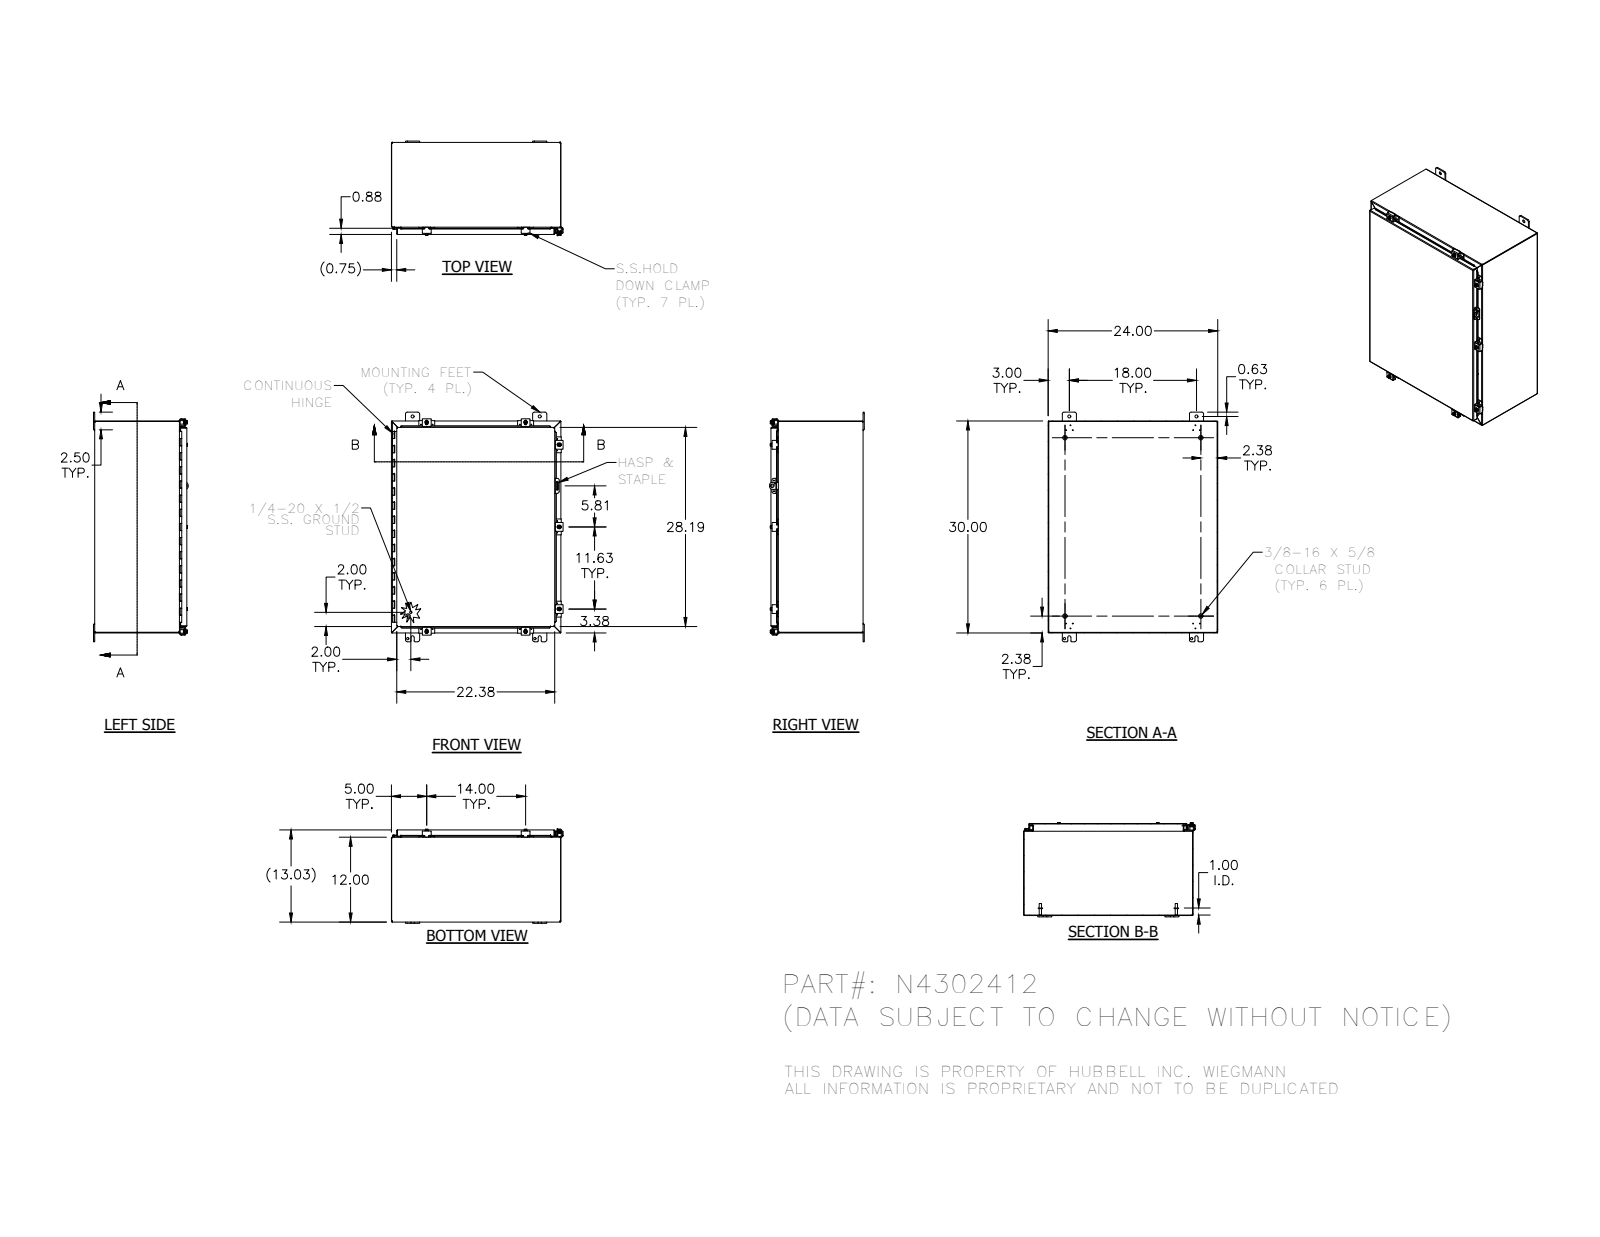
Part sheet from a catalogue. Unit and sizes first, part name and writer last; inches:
Units: inches
Overall size (bounding box): 32.5 × 24.311 × 13.41
Round holes (diameter × count): ⌀0.11 ×17, ⌀0.12 ×12, ⌀0.211 ×7, ⌀0.281 ×7, ⌀0.3 ×7, ⌀0.313 ×4, ⌀0.438 ×4, ⌀0.125 ×1, ⌀0.156 ×1, ⌀0.5 ×1
Round bosses / shafts (diameter × count): ⌀0.25 ×9, ⌀0.52 ×7, ⌀0.5 ×7, ⌀0.35 ×7, ⌀0.625 ×4, ⌀0.33 ×4, ⌀0.115 ×2, ⌀0.337 ×1
Partial cylindrical surfaces — rounded edges, fillets, slot ends (radius × count): R0.03 ×83, R0.062 ×41, R0.125 ×37, R0.25 ×33, R0.031 ×23, R0.105 ×23, R0.063 ×14, R0.141 ×14
Main face-to-face distances: 0.074, 12.959, 23.926, 12.885, 13.033, 29.926, 23.852, 24, 29.852, 30
Hole centre spacings: 18, 0.876, 0.759, 0.94, 0.969, 1.995, 17.37, 18.339
Volume: 240.8 in³ · Surface area: 6 337 in²
Bodies: 52 solids, 2311 faces (889 planar, 1039 cylindrical, 383 other)
Part name (STEP PRODUCT): 32911_1; 388116_1; 28x22_1; HFW30825-4_1 (+8 more)
STEP written by: SolidWorks 2014 (AUTOMOTIVE_DESIGN)
